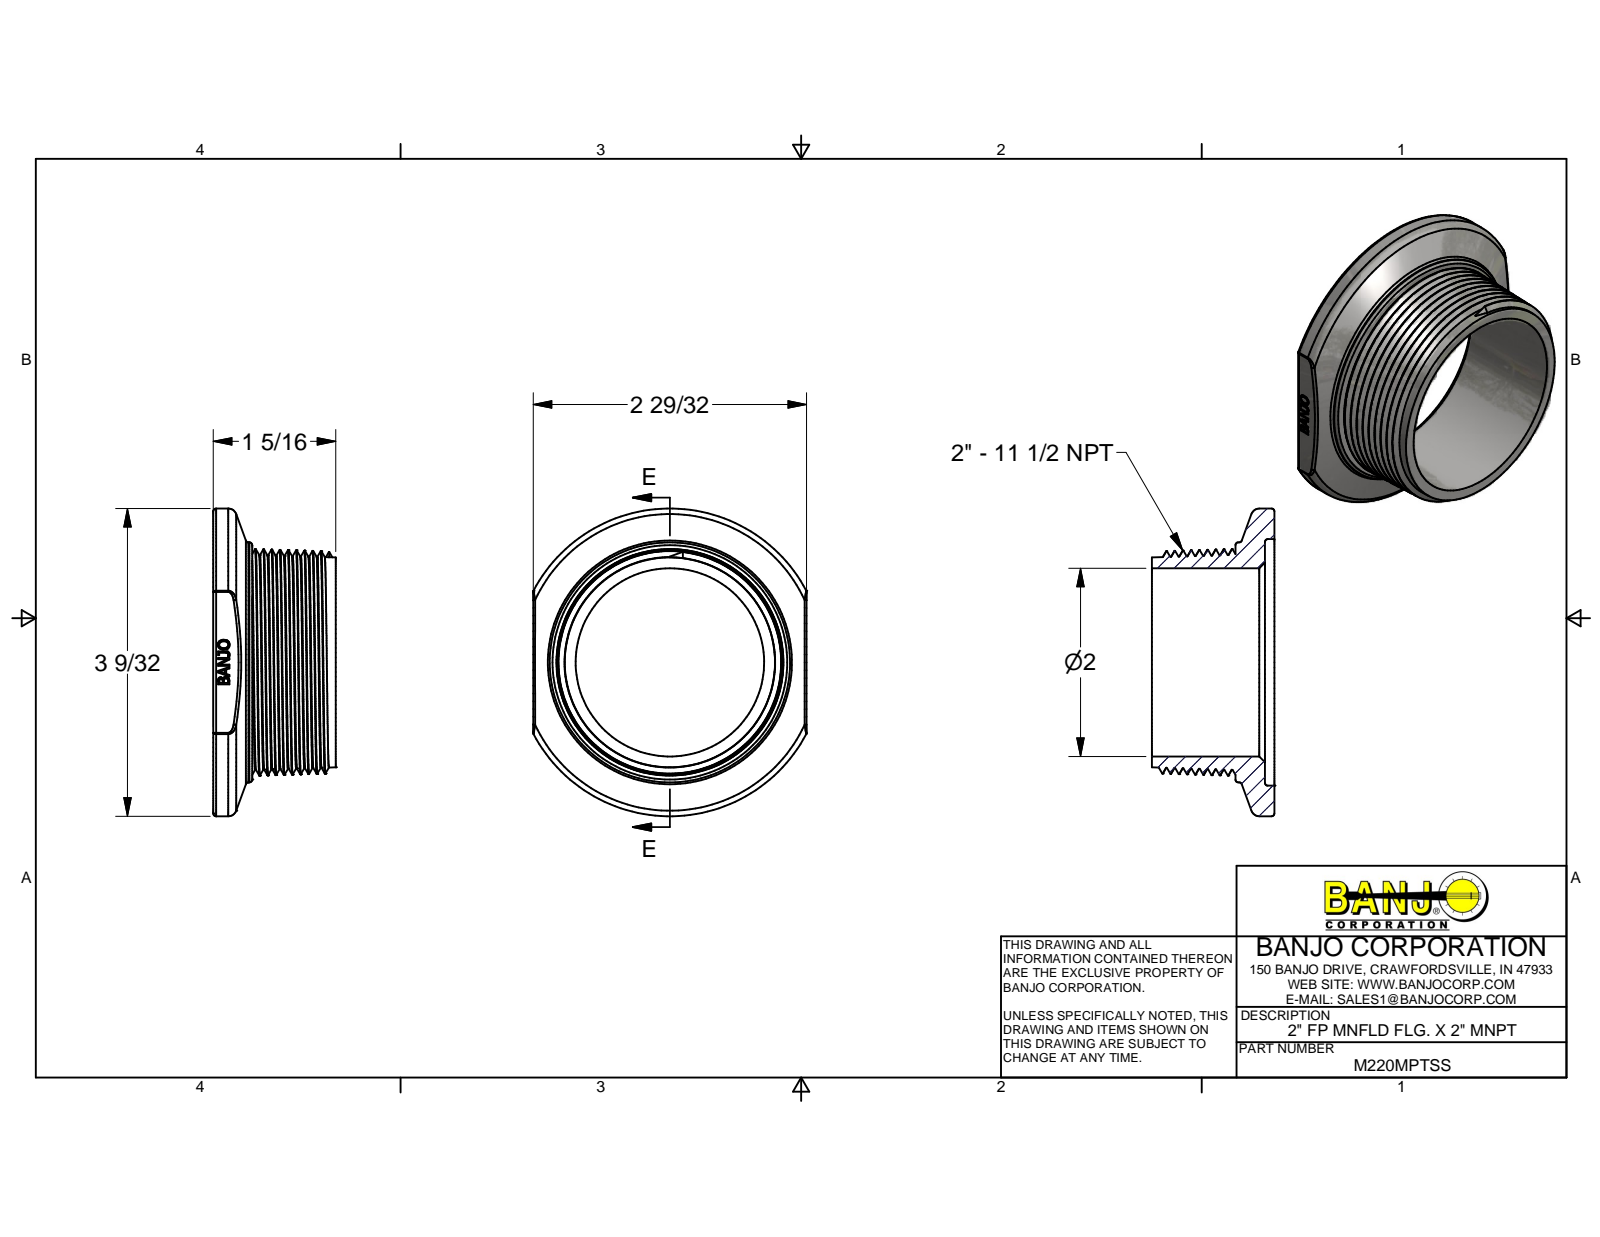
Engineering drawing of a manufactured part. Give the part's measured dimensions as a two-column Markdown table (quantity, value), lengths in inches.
| quantity | value |
| --- | --- |
| part name | M220MPTSS |
| STEP written by | Autodesk Inventor 2013 (AUTOMOTIVE_DESIGN) |
| units | inches |
| bodies | 1 solid, 279 faces (127 planar, 11 cylindrical, 141 other) |
| overall size | 3.27 × 2.9 × 1.3 |
| volume | 2.356 in³ |
| surface area | 31.71 in² |
| round holes (diameter × count) | 2 × 1, 2.62 × 1 |
| round bosses / shafts (diameter × count) | 2.55 × 1 |
| partial cylindrical surfaces (radius × count) | 0.03 × 6, 1.635 × 1 |
| main face-to-face distances | 0.1, 1.2, 1.3, 0.887, 0.313, 0.413, 2.9, 0.03, 2.87, 2.84 |
